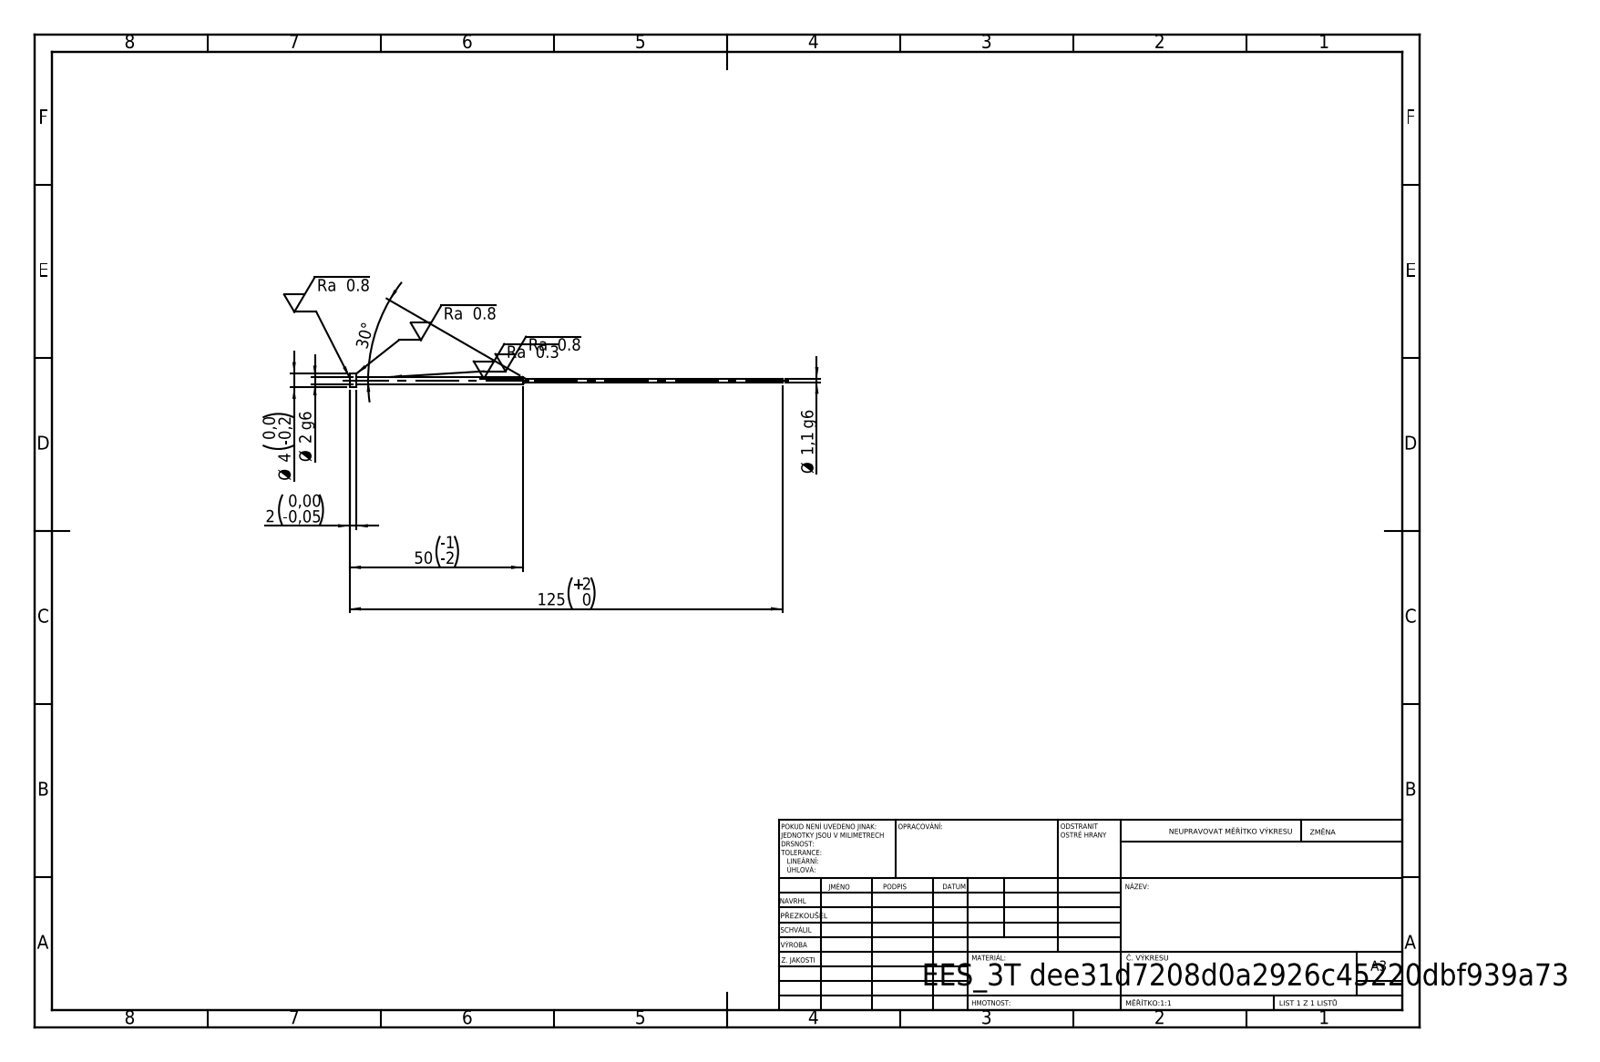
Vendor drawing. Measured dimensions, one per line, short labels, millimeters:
written by: SolidWorks 2019 (CONFIG_CONTROL_DESIGN)
unit: mm
bodies: 1 solid, 11 faces (3 planar, 6 cylindrical, 2 other)
size: 125 × 4 × 4
volume: 248 mm³; area: 611 mm²
bosses: 1× ⌀4, 1× ⌀2, 1× ⌀1.1
face distances: 2, 123, 125
